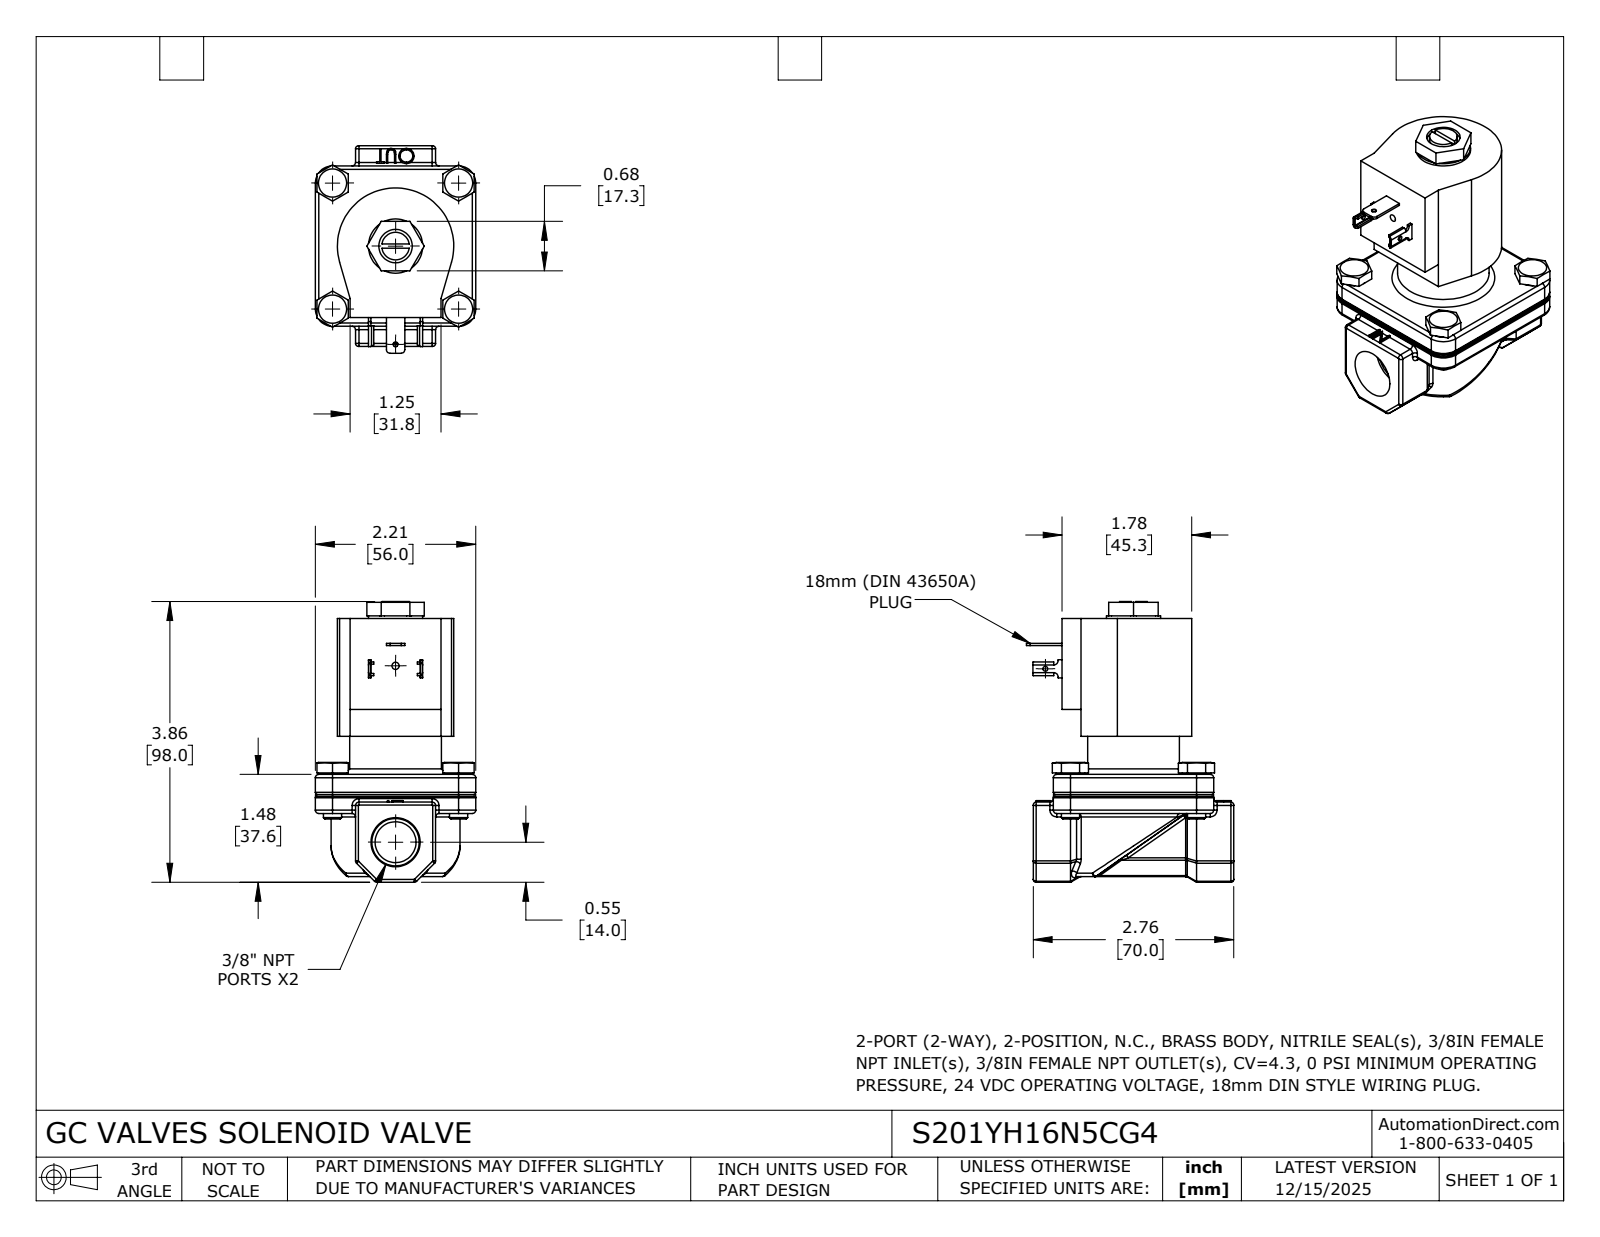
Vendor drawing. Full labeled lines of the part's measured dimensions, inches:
Part name (STEP PRODUCT): S201YH16N5CG4
STEP written by: SolidWorks 2024 (CONFIG_CONTROL_DESIGN)
Units: inches
Bodies: 1 solid, 483 faces (204 planar, 153 cylindrical, 126 other)
Overall size (bounding box): 3.857 × 2.851 × 2.205
Volume: 9.705 in³ · Surface area: 40.43 in²
Round holes (diameter × count): ⌀0.066 ×1, ⌀0.067 ×1, ⌀0.1 ×1, ⌀0.46 ×1, ⌀0.562 ×1
Round bosses / shafts (diameter × count): ⌀0.388 ×4, ⌀0.25 ×4, ⌀1.26 ×1, ⌀0.746 ×1, ⌀0.38 ×1
Partial cylindrical surfaces — rounded edges, fillets, slot ends (radius × count): R0.047 ×57, R0.04 ×12, R0.006 ×4, R0.031 ×4, R0.041 ×4, R0.234 ×4, R0.236 ×4, R0.05 ×2
Main face-to-face distances: 2.143, 0.551, 1.654, 2.205, 0.537, 2.68, 0.276, 2.48, 1.06, 0.523
Hole centre spacings: 1.35, 2.423
